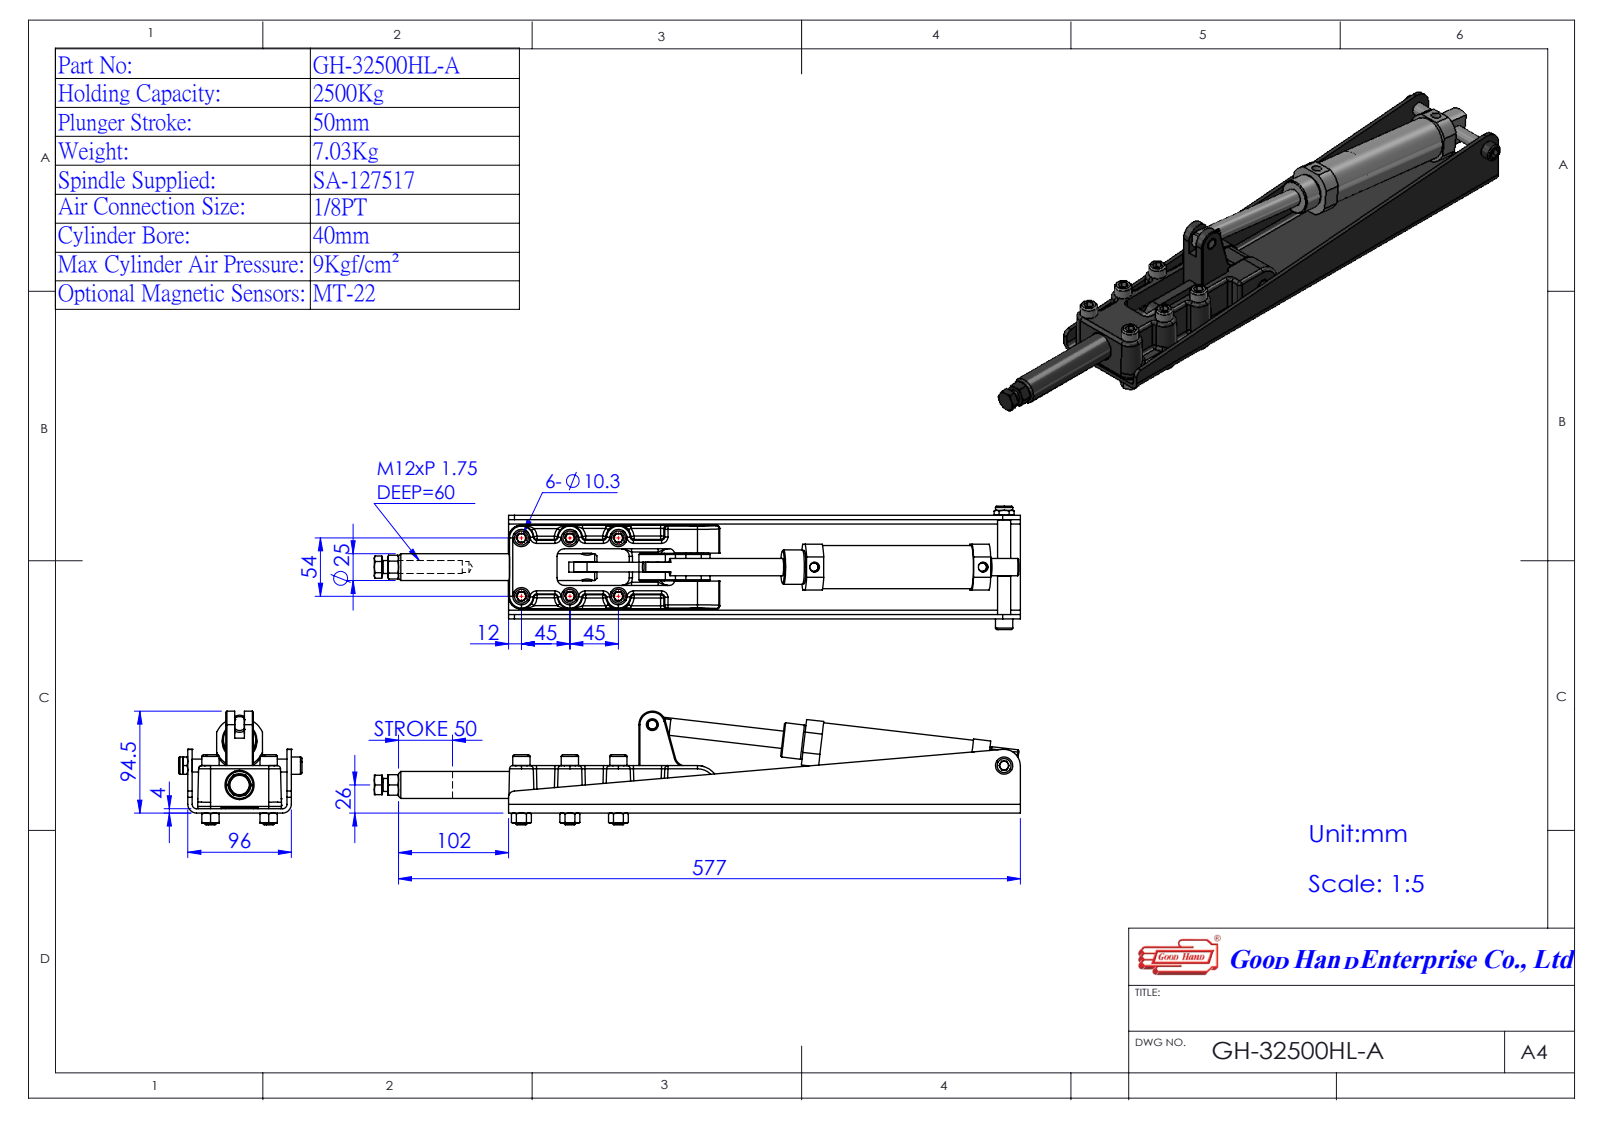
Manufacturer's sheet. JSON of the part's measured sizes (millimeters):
{"part_name": "GH-32500HL-A(簡化); SDA serial cylinder A_SDA 40×100-1^GH-32500HL-A(簡化); 43250005-1^GH-32500HL-A(簡化); Group7^GH-32500HL-A(簡化) (+4 more)", "step_written_by": "SolidWorks 2016 (AUTOMOTIVE_DESIGN)", "units": "millimeters", "bodies": {"solids": 7, "faces": 1321, "planar": 688, "cylindrical": 290, "other": 343}, "overall_size": [599.5, 114.56, 105.5], "volume_mm3": 998208, "surface_area_mm2": 327859, "round_holes": [[7, 2], [7.9, 2], [2.68, 1], [9, 1], [10.2, 1], [12, 1], [15, 1], [16, 1], [18, 1], [25, 1], [38, 1]], "round_bosses_or_shafts": [[16, 8], [10, 7], [40, 1], [38, 1], [32, 1], [31, 1], [18, 1], [12, 1]], "partial_cylinders_radius": [[3, 29], [7, 6], [8, 5], [12.5, 3], [0.28, 2], [0.34, 2], [0.35, 2], [0.58, 2]], "face_to_face_distances": [4, 92, 88, 96, 31, 61, 27, 65, 5, 35.2], "hole_center_spacings": [37.5, 56.14, 62.62, 69.7, 157.5, 223.54, 261.02, 269.52]}
